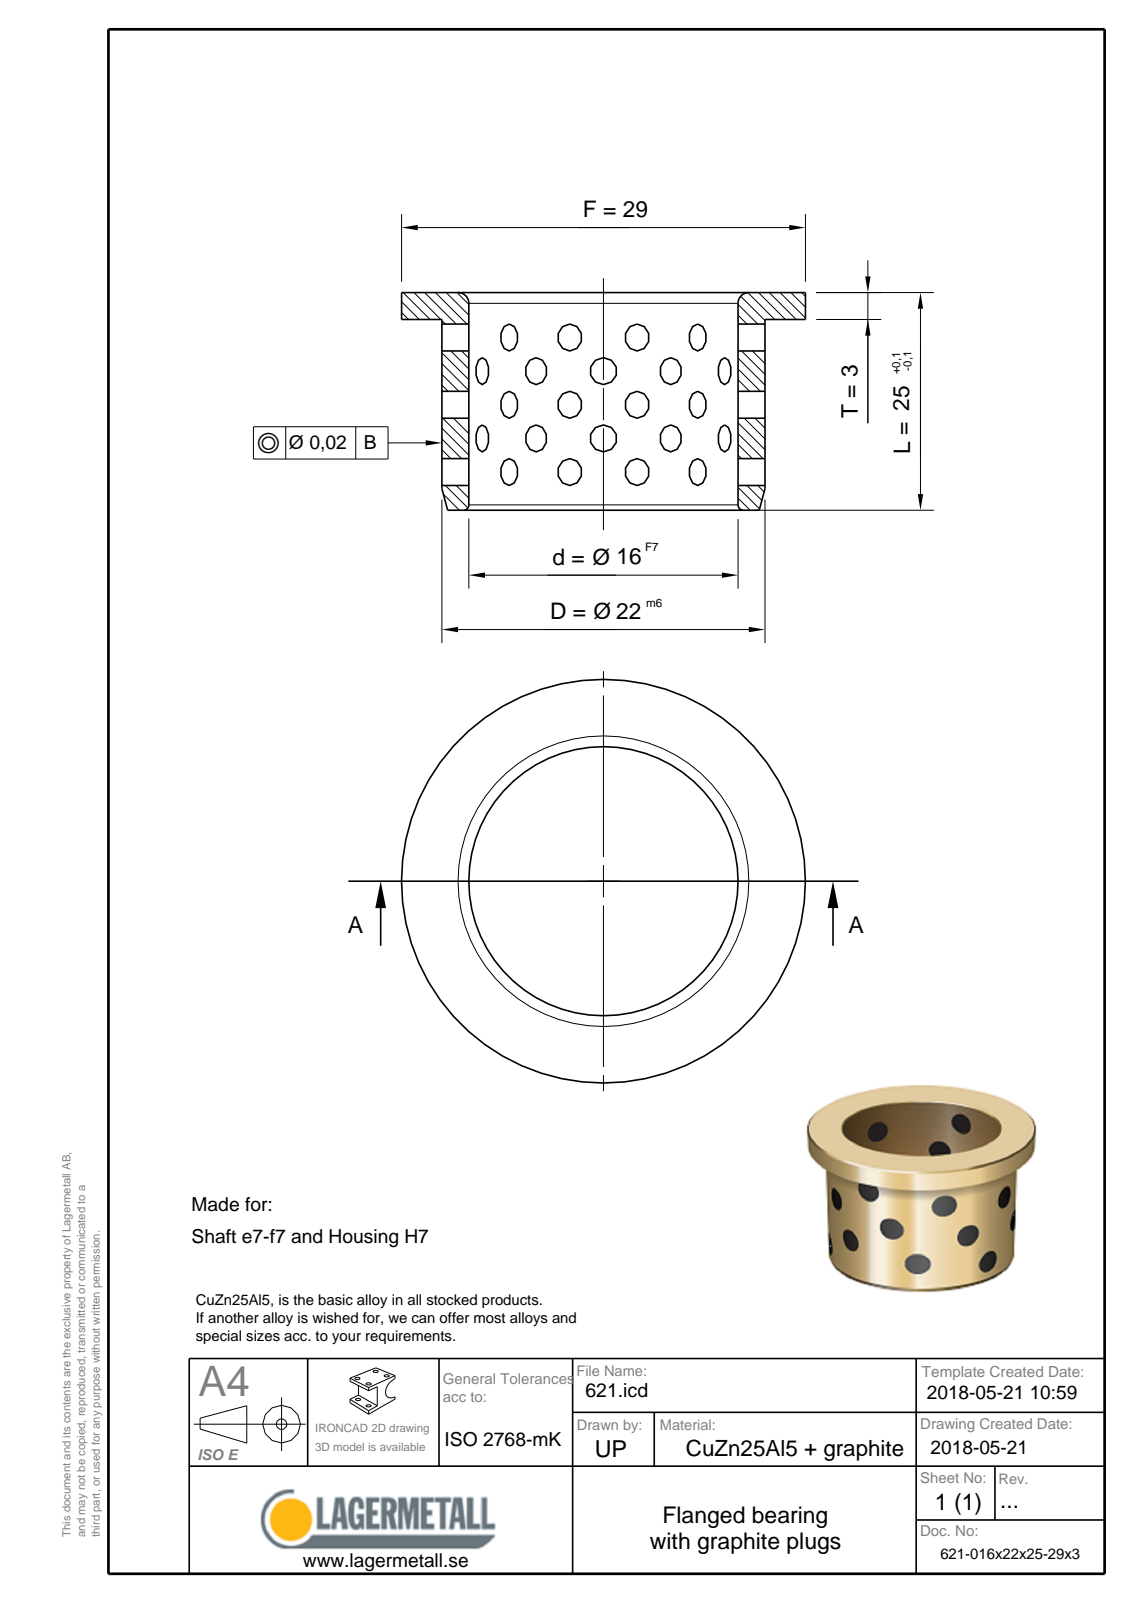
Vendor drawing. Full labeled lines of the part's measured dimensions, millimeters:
Part name (STEP PRODUCT): 621-016x22x25-29x3
STEP written by: Spatial InterOp 3D (CONFIG_CONTROL_DESIGN)
Units: millimetres
Bodies: 1 solid, 9 faces (3 planar, 3 cylindrical, 3 other)
Overall size (bounding box): 29 × 29 × 25
Volume: 5 220 mm³ · Surface area: 3 862 mm²
Round holes (diameter × count): ⌀16 ×1
Round bosses / shafts (diameter × count): ⌀29 ×1, ⌀22 ×1
Main face-to-face distances: 3, 22, 25
